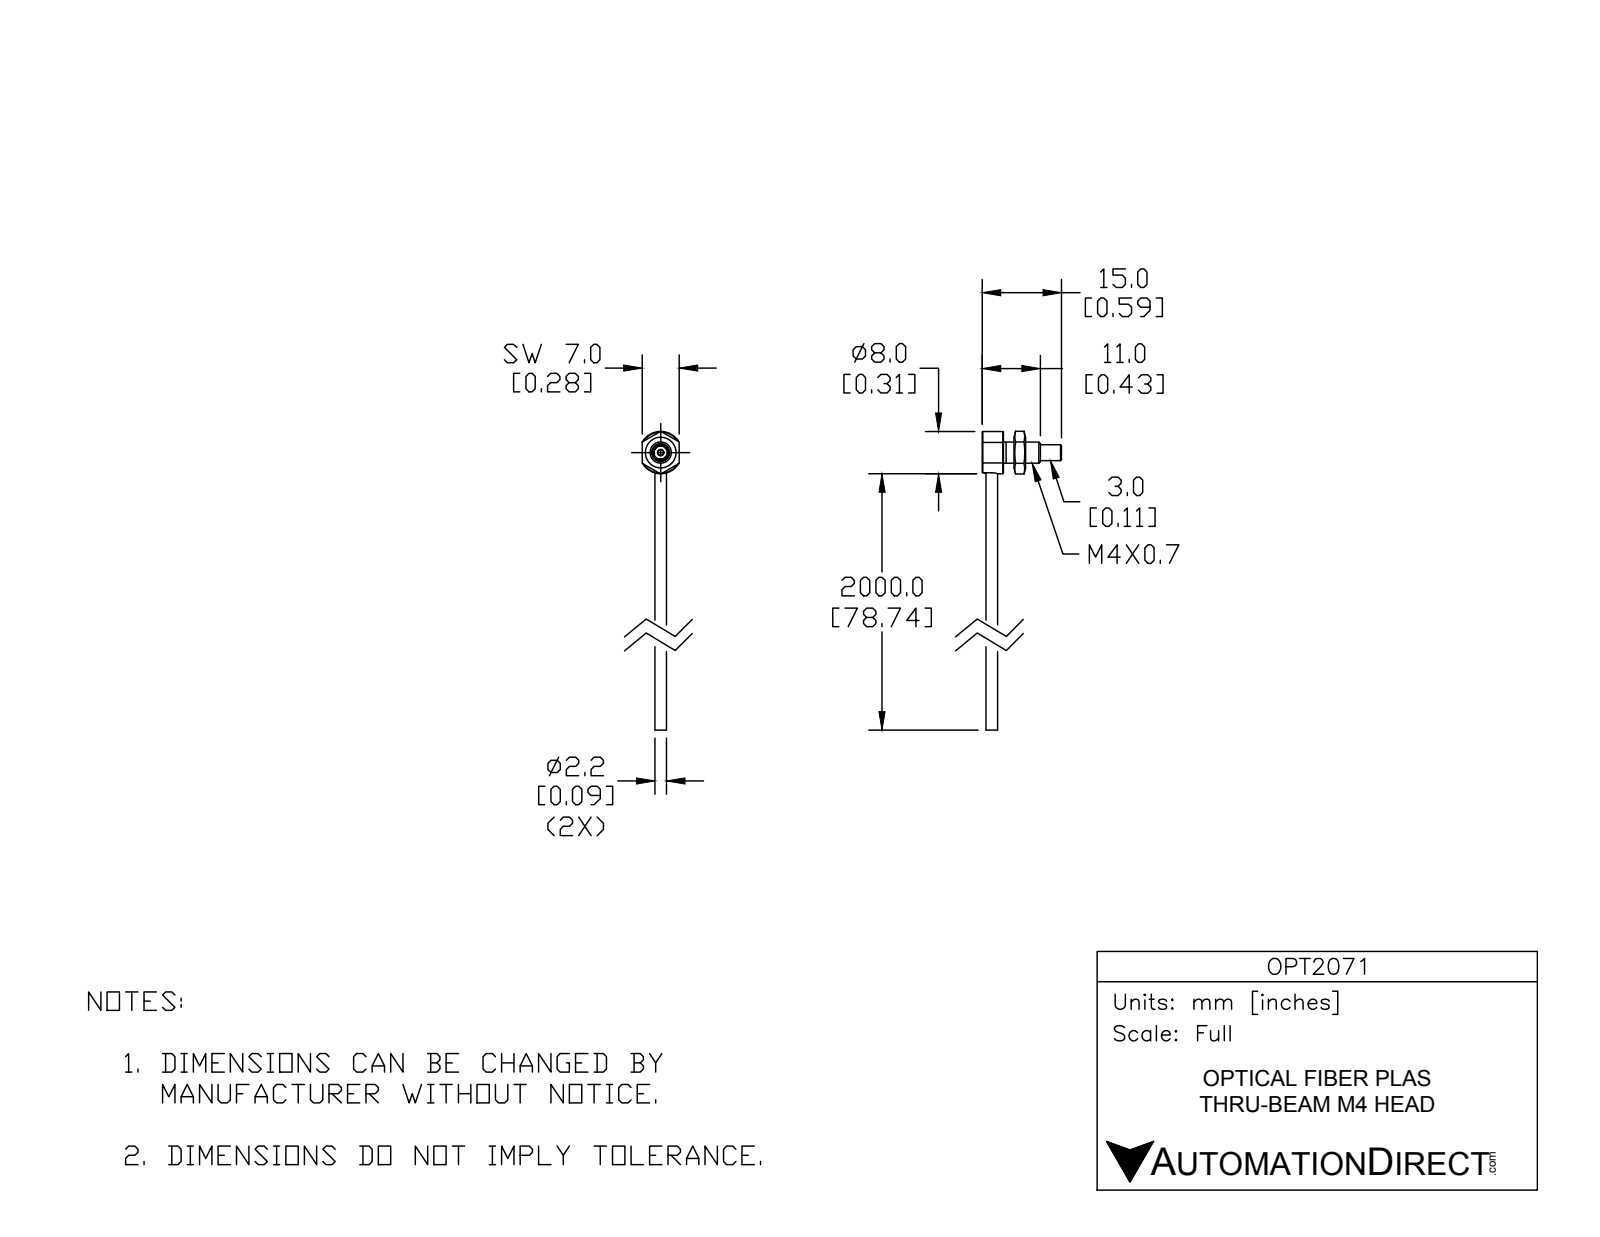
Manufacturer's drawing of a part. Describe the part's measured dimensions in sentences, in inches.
The part is named "OPT2071". Its 3-D file was written by "SolidWorks 2014 (AUTOMOTIVE_DESIGN)". It is 1 solid with 60 faces: 24 planar, 19 cylindrical and 17 other. Overall it measures 2.226 by 0.591 by 0.276 inches. Its volume is 0.033 cubic inches and its surface area 1.145 square inches. Round holes: 1 of diameter 0.236. Round bosses or shafts: 1 of diameter 0.157, 1 of diameter 0.118, 1 of diameter 0.087, 1 of diameter 0.047. Partial cylindrical surfaces (rounded edges, fillets, slot ends): 1 of radius 0.047, 1 of radius 0.156, 1 of radius 0.157. The main face-to-face distances are 0.276, 0.154, 0.157, 0.236, 0.323, 0.232, 0.319, 0.079, 0.165, 0.087.
